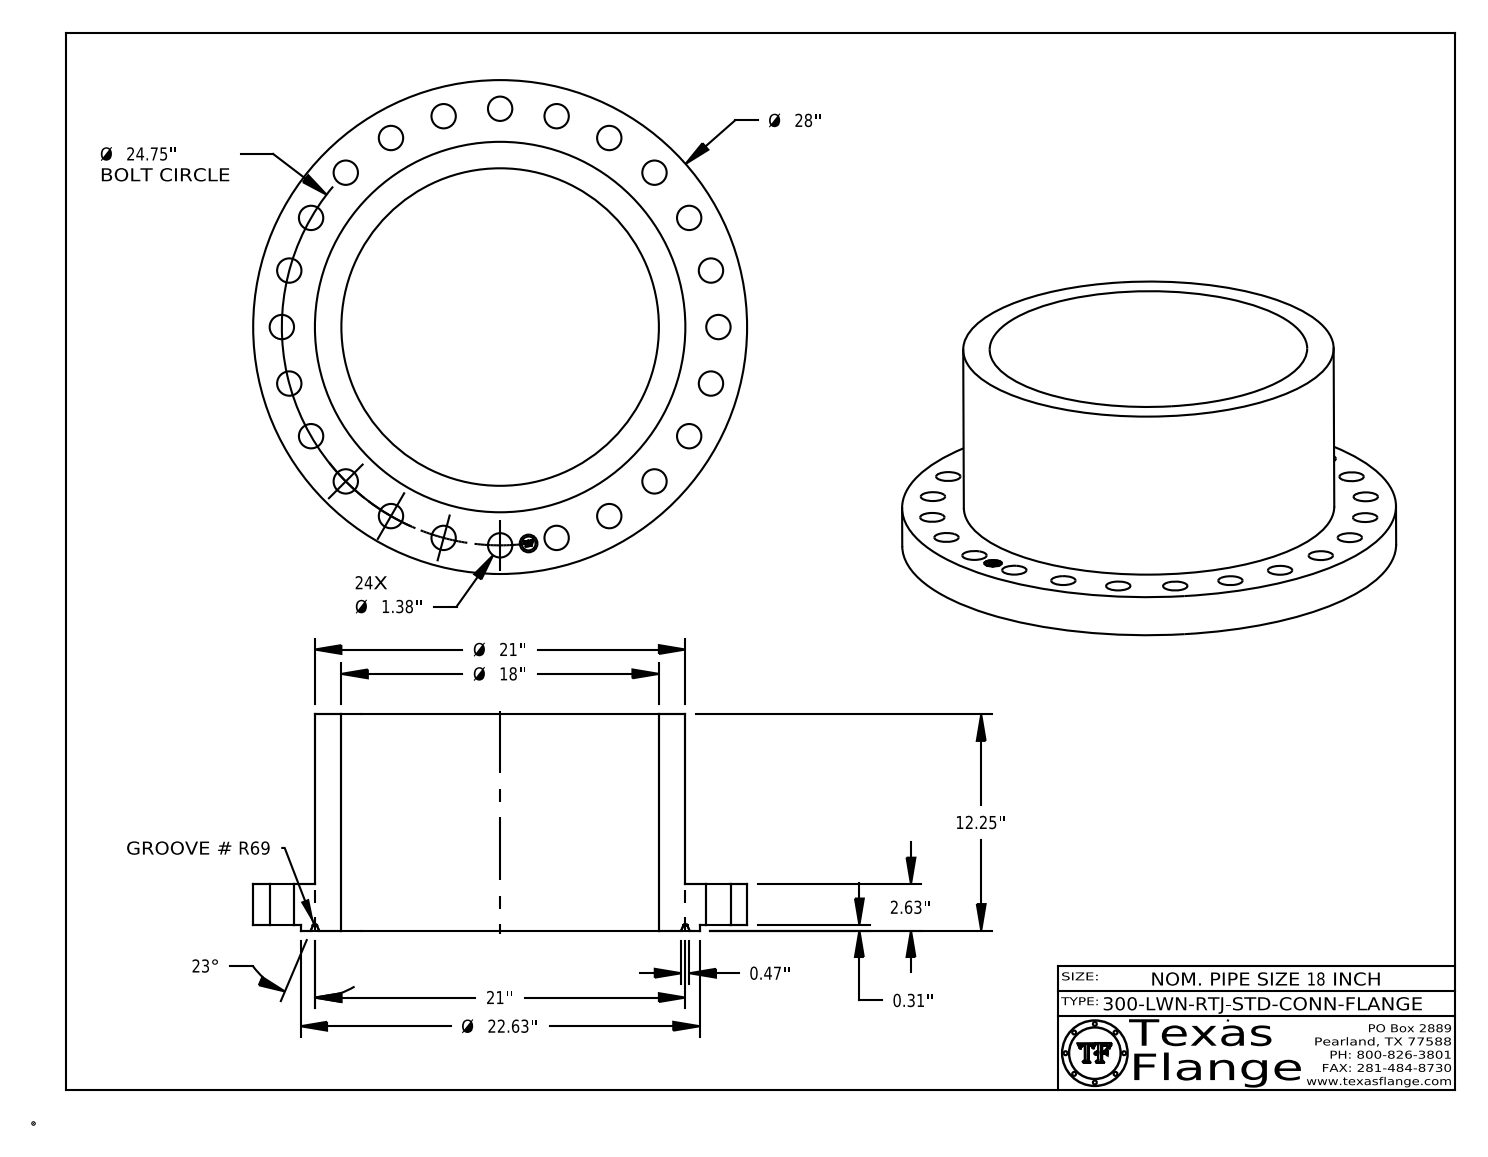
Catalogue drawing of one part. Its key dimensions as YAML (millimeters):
part_name: "18-300-LWN-RTJ-STD-CONN-FLANGE"
step_written_by: "CATIA V5 STEP AP214 (AUTOMOTIVE_DESIGN)"
units: millimeters
bodies: {solids: 1, faces: 455, planar: 371, cylindrical: 76, other: 8}
overall_size: [711.2, 711.2, 311.2]
volume: 27480000
surface_area: 1595000
round_holes:
  - {diameter: 35.1, count: 24}
  - {diameter: 25.4, count: 1}
  - {diameter: 457.2, count: 1}
round_bosses_or_shafts:
  - {diameter: 1.5, count: 8}
  - {diameter: 711.2, count: 1}
  - {diameter: 574.7, count: 1}
  - {diameter: 533.4, count: 1}
  - {diameter: 20, count: 1}
face_to_face_distances: [58.9, 8, 66.8, 311.2, 303.2, 244.3, 66.7, 58.8, 244.5, 7.6]
hole_center_spacings: [314.3, 240.6, 382.7, 444.5, 544.4, 580.8, 607.2, 82]
